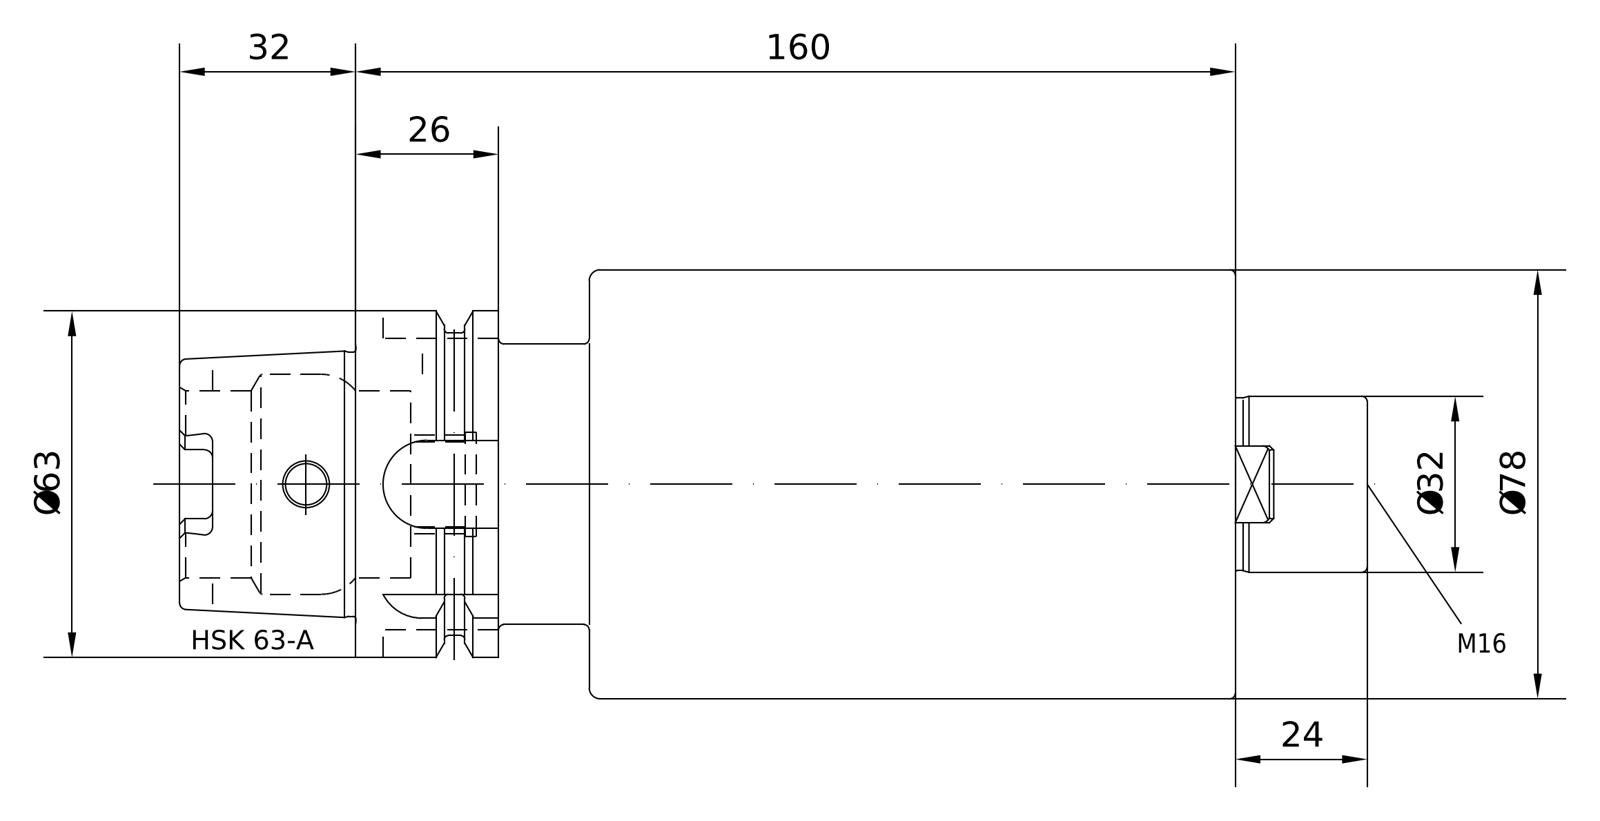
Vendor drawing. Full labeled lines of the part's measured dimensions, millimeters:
Part name (STEP PRODUCT): A63-052-32
STEP written by: PRO/ENGINEER BY PARAMETRIC TECHNOLOGY CORPORATION, 2010430 (CONFIG_CONTROL_DESIGN)
Units: millimetres
Bodies: 1 solid, 198 faces (70 planar, 54 cylindrical, 74 other)
Overall size (bounding box): 216 × 78 × 78
Volume: 692 337 mm³ · Surface area: 65 519 mm²
Round holes (diameter × count): ⌀7.5 ×1, ⌀10 ×1, ⌀14 ×1, ⌀16 ×1, ⌀16.92 ×1, ⌀18.32 ×1, ⌀18.66 ×1, ⌀34 ×1, ⌀40 ×1
Round bosses / shafts (diameter × count): ⌀78 ×1, ⌀63 ×1, ⌀55 ×1, ⌀51 ×1, ⌀48.04 ×1, ⌀32 ×1, ⌀18 ×1
Partial cylindrical surfaces — rounded edges, fillets, slot ends (radius × count): R1.5 ×6, R3 ×4, R8 ×1, R8.02 ×1, R9.02 ×1
Main face-to-face distances: 117.5, 42.5, 160, 26, 16.5, 134, 10, 184, 158, 141.5
